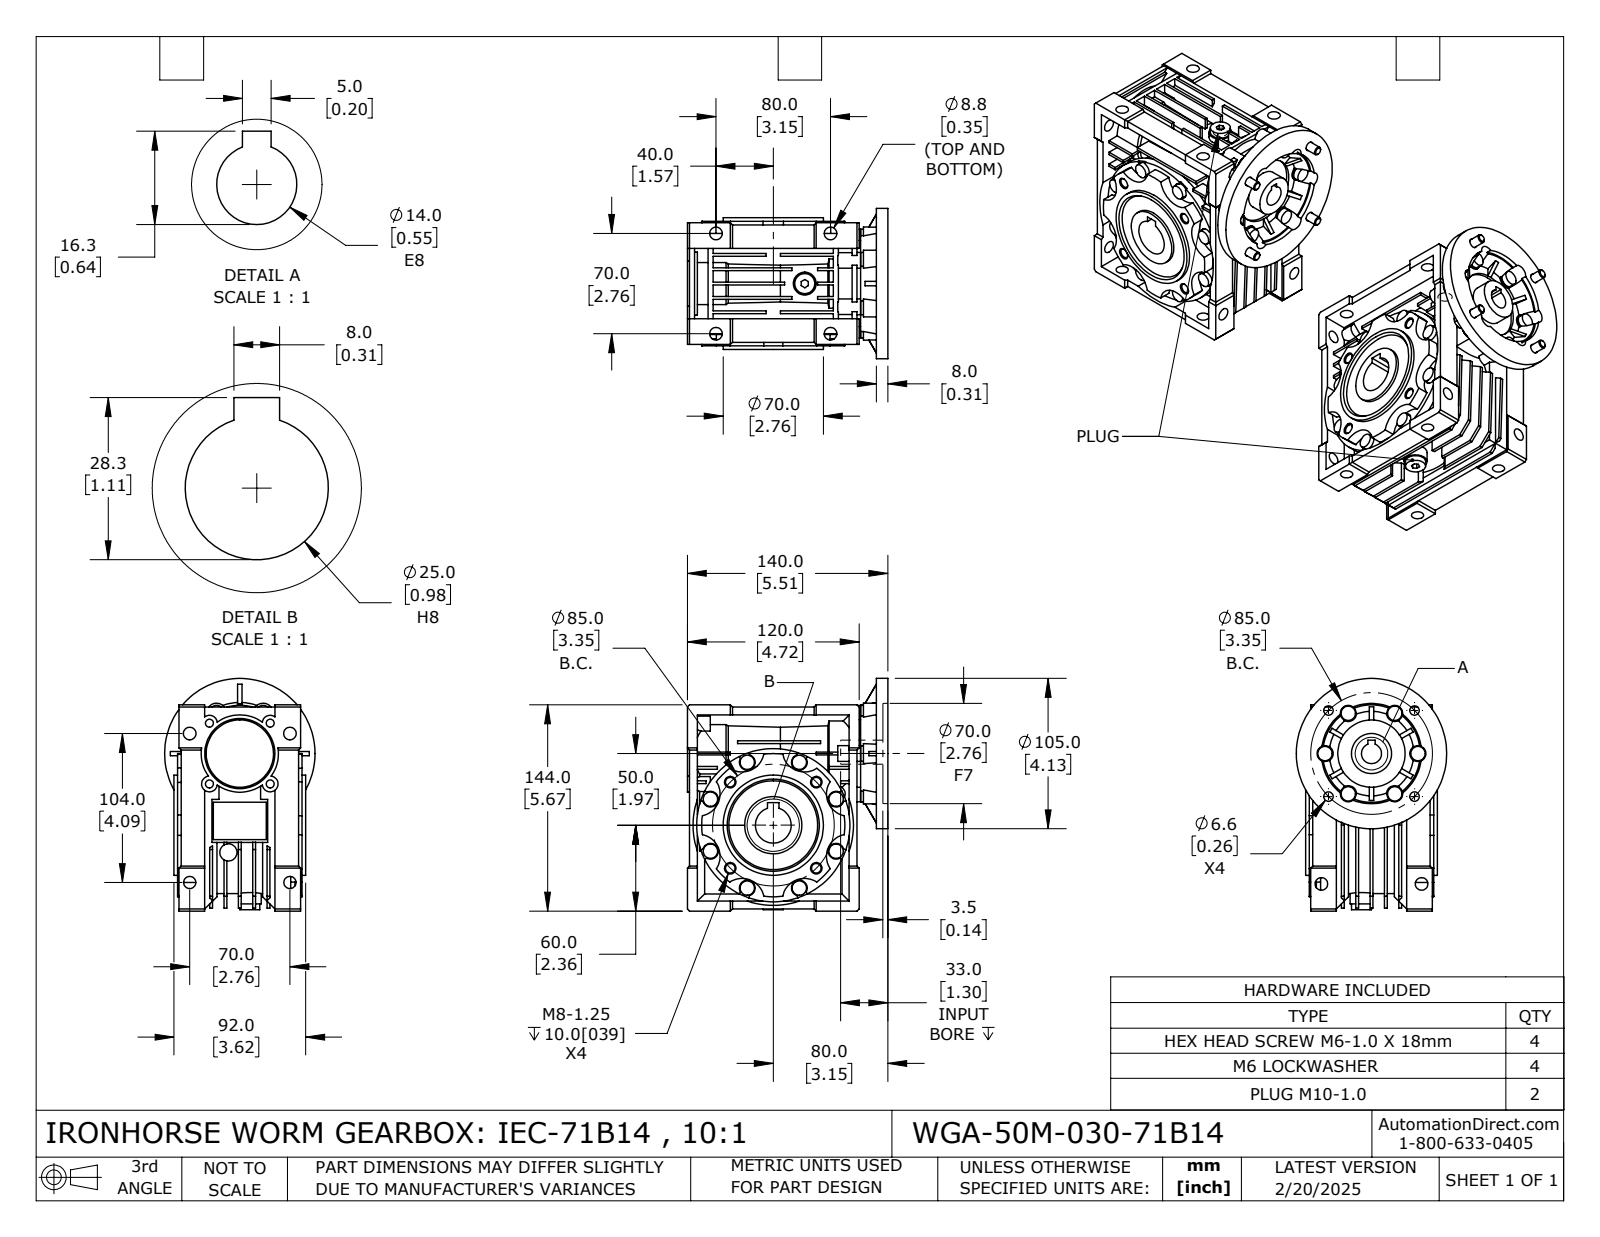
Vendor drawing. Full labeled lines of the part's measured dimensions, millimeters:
Part name (STEP PRODUCT): WGA-50M-030-71B14
STEP written by: SolidWorks 2024 (CONFIG_CONTROL_DESIGN)
Units: millimetres
Bodies: 15 solids, 1132 faces (615 planar, 372 cylindrical, 145 other)
Overall size (bounding box): 162.5 × 148.5 × 105
Volume: 1 065 000 mm³ · Surface area: 235 209 mm²
Round holes (diameter × count): ⌀8.8 ×8, ⌀8.5 ×6, ⌀5.55 ×4, ⌀6.1 ×4, ⌀6.6 ×4, ⌀6.65 ×2, ⌀6.65 ×2, ⌀9 ×2, ⌀14 ×1, ⌀15 ×1, ⌀25 ×1, ⌀28 ×1
Round bosses / shafts (diameter × count): ⌀10 ×14, ⌀12.2 ×4, ⌀6 ×4, ⌀16 ×2, ⌀14 ×2, ⌀9.8 ×2, ⌀8.3 ×2, ⌀107 ×1
Partial cylindrical surfaces — rounded edges, fillets, slot ends (radius × count): R5.5 ×18, R6 ×8, R15 ×8, R15.5 ×8, R5.75 ×6, R7 ×6, R20.76 ×1, R35 ×1
Main face-to-face distances: 8, 2, 10, 7, 1.5, 5.5, 20, 12, 55, 35
Hole centre spacings: 42.5, 52.02, 60.1, 70, 12.5, 30, 42.42, 72.49
